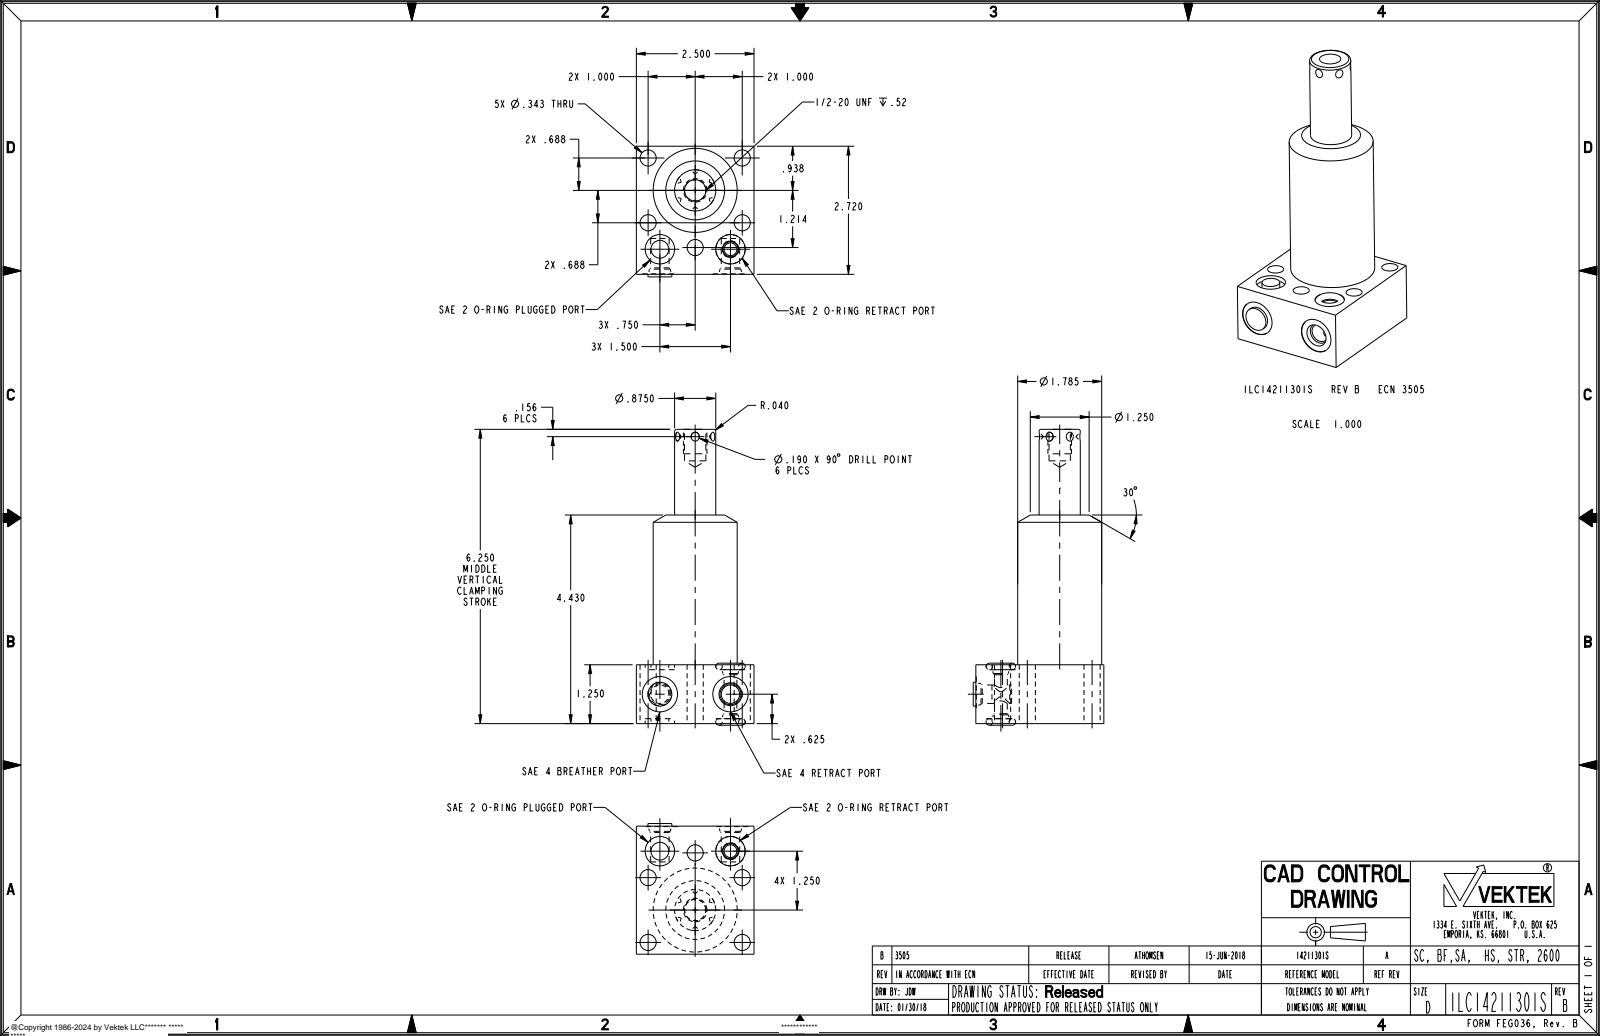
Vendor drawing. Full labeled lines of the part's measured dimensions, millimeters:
Part name (STEP PRODUCT): ILC14211301S
STEP written by: PRO/ENGINEER BY PARAMETRIC TECHNOLOGY CORPORATION, 2013320 (AUTOMOTIVE_DESIGN)
Units: millimetres
Bodies: 3 solids, 109 faces (21 planar, 46 cylindrical, 42 other)
Overall size (bounding box): 159.6 × 70.5 × 63.5
Volume: 270 400 mm³ · Surface area: 39 740 mm²
Round holes (diameter × count): ⌀8.7 ×5, ⌀10 ×2, ⌀15.9 ×2, ⌀19.1 ×2, ⌀6.9 ×1, ⌀11.5 ×1
Round bosses / shafts (diameter × count): ⌀45.3 ×1, ⌀22.2 ×1, ⌀12.9 ×1, ⌀12.7 ×1, ⌀9.6 ×1
Main face-to-face distances: 63.5, 31.8, 69.1, 2.7, 29.1, 68.8, 112.5, 80.8, 26.4, 109.9
Hole centre spacings: 30.8, 15.6, 19.1, 28.7, 35, 37, 38.1, 46.7
